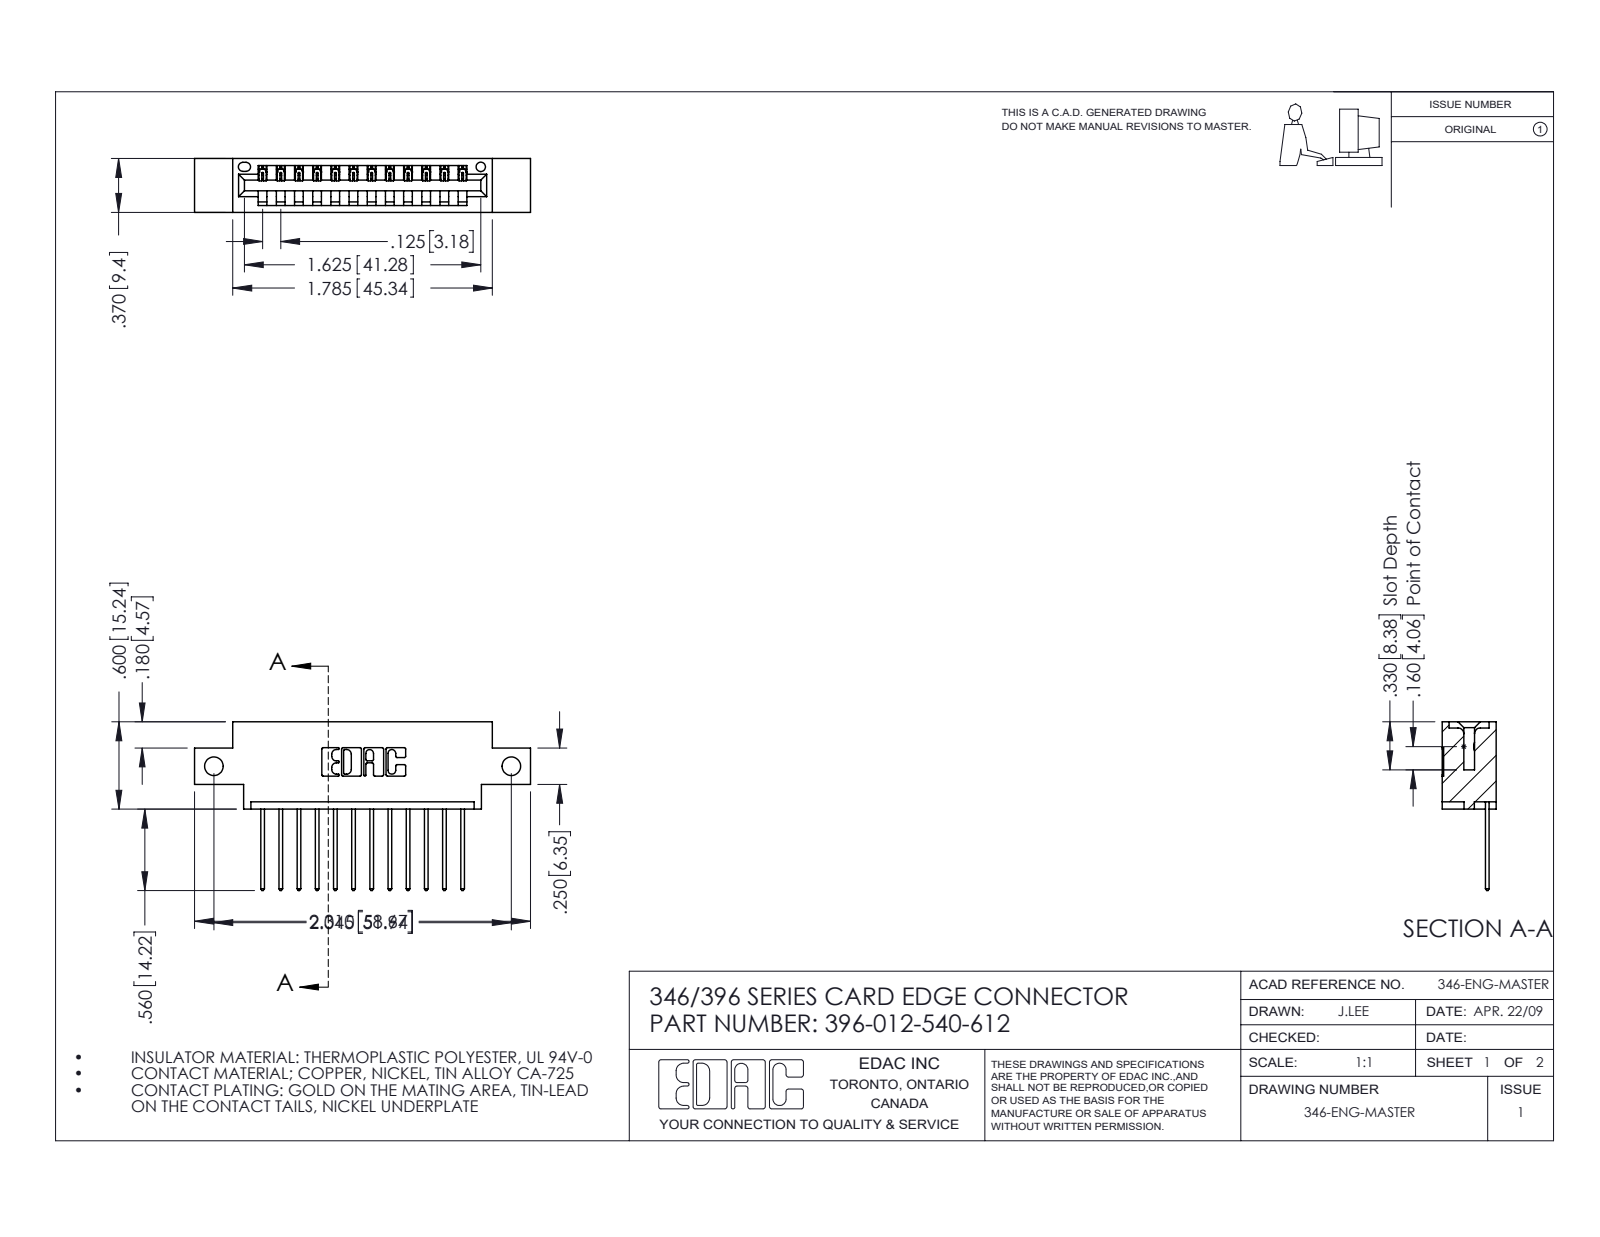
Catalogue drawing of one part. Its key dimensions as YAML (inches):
part_name: "346 Part_0.170 Offset - Side Mount; 396-012-540-612; 345-292-001_345-293-140"
step_written_by: "SolidWorks 2016 (CONFIG_CONTROL_DESIGN)"
units: inches
bodies: {solids: 13, faces: 822, planar: 560, cylindrical: 262, other: 0}
overall_size: [2.31, 1.16, 0.37]
volume: 0.316
surface_area: 9.748
round_holes:
  - {diameter: 0.128, count: 2}
  - {diameter: 0.064, count: 1}
partial_cylinders:
  - {radius: 0.006, count: 24}
  - {radius: 0.01, count: 24}
  - {radius: 0.01, count: 22}
  - {radius: 0.007, count: 6}
  - {radius: 0.031, count: 6}
  - {radius: 0.026, count: 3}
  - {radius: 0.031, count: 2}
  - {radius: 0.04, count: 2}
face_to_face_distances: [0.25, 0.37, 0.048, 0.322, 0.072, 0.298, 0.025, 0.148, 0.222, 0.1]
hole_center_spacings: [2.045]
